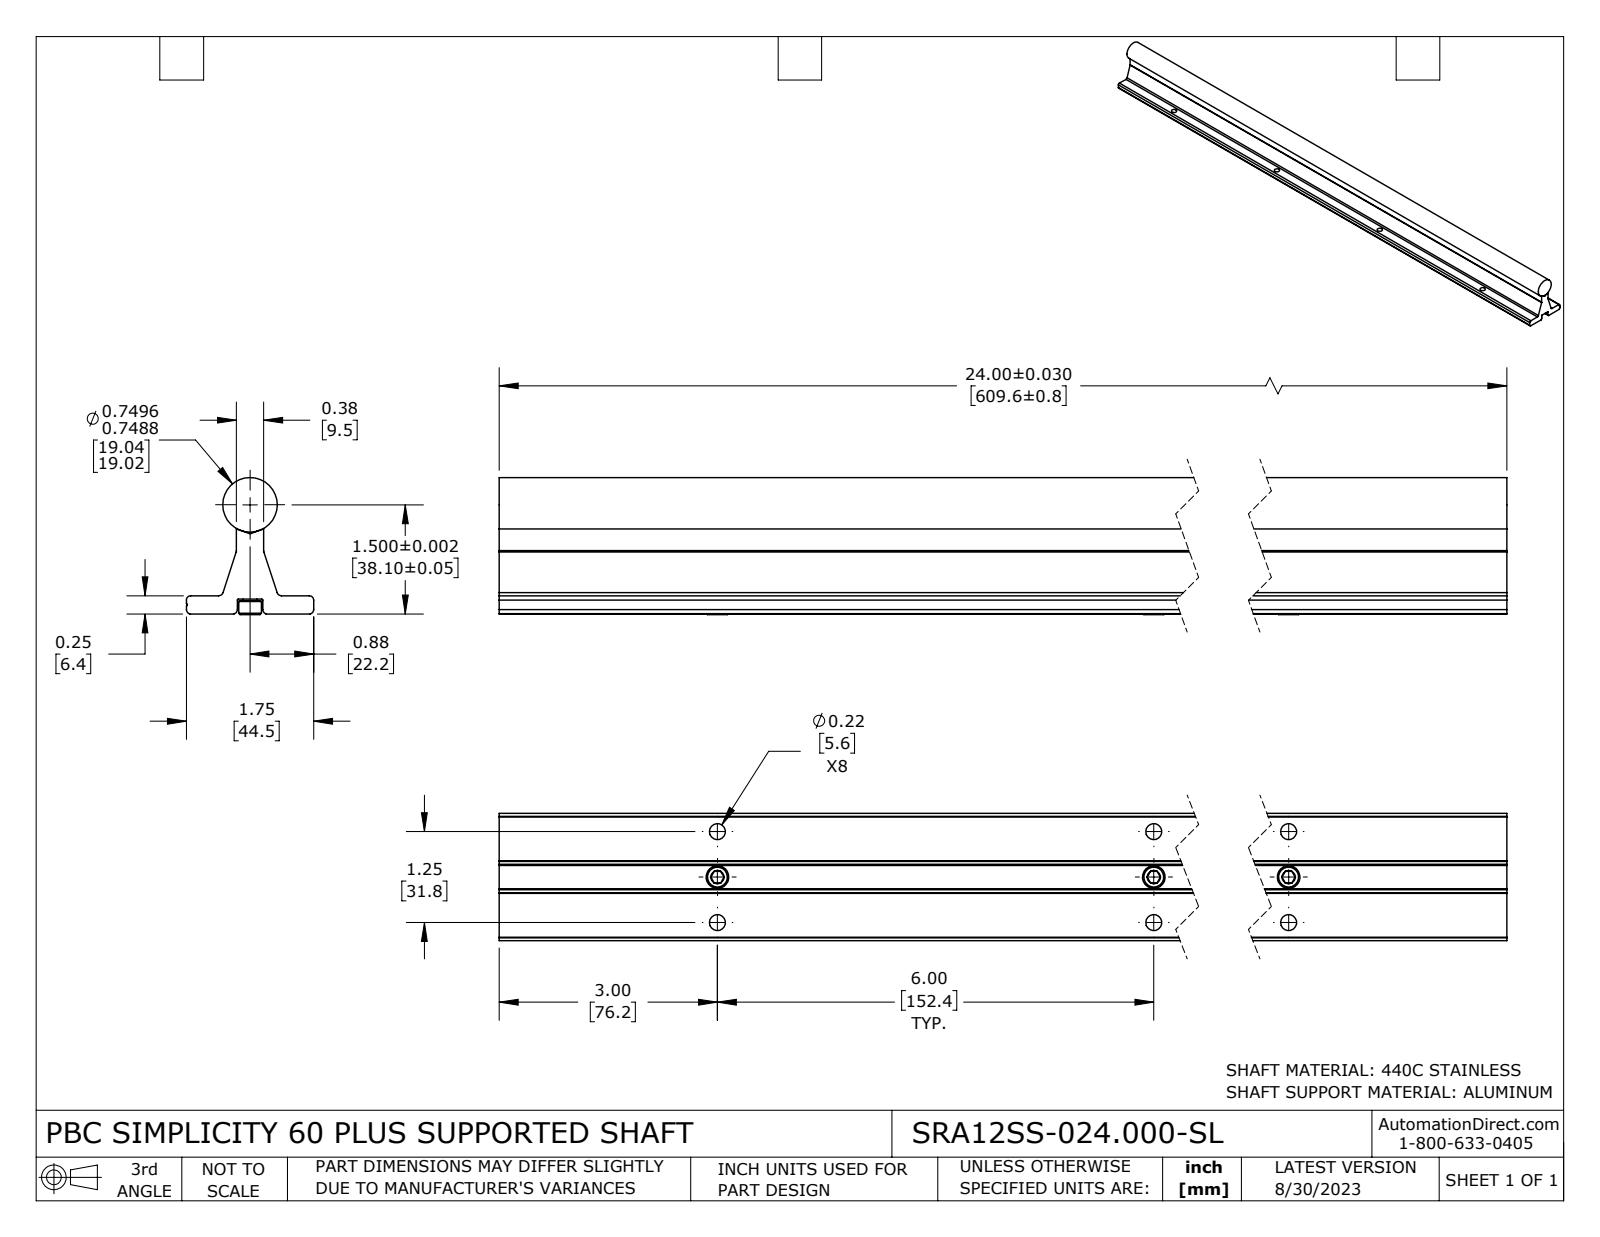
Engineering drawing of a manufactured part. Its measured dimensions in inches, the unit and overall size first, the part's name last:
Units: inches
Overall size (bounding box): 24 × 1.885 × 1.75
Round holes (diameter × count): ⌀0.221 ×12, ⌀0.169 ×4, ⌀0.25 ×4
Round bosses / shafts (diameter × count): ⌀0.312 ×4, ⌀0.19 ×4, ⌀0.75 ×1
Partial cylindrical surfaces — rounded edges, fillets, slot ends (radius × count): R0.06 ×6, R0.015 ×2, R0.062 ×2, R0.063 ×2
Main face-to-face distances: 0.25, 0.205, 0.045, 0.375, 0.012, 0.363, 0.688, 0.7, 1.05, 1.063
Hole centre spacings: 6.033, 6, 0.625, 12.016, 6.129, 12, 1.25, 12.065
Volume: 30.08 in³ · Surface area: 206 in²
Bodies: 6 solids, 201 faces (71 planar, 70 cylindrical, 60 other)
Part name (STEP PRODUCT): SRA12SS-024.000-SL
STEP written by: SolidWorks 2021 (CONFIG_CONTROL_DESIGN)
